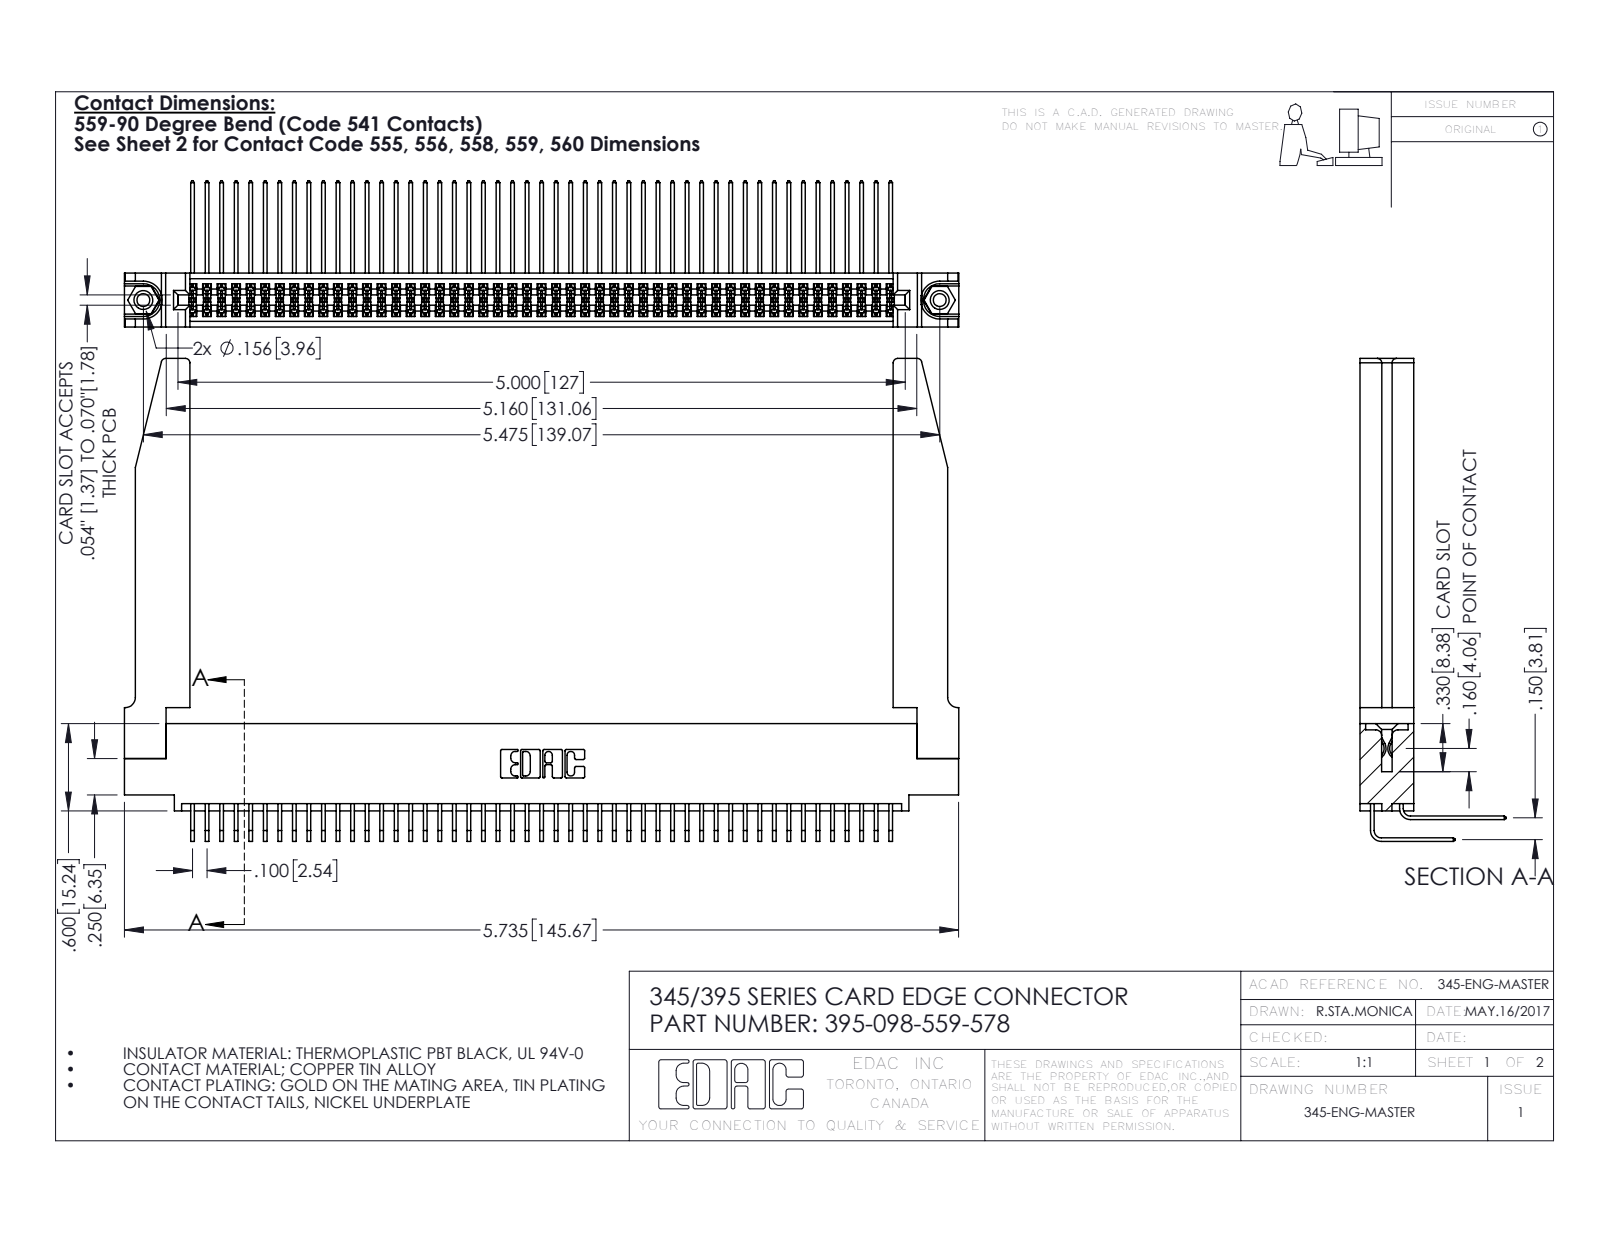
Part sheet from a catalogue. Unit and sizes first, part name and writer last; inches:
Units: inches
Overall size (bounding box): 5.736 × 3.319 × 1.005
Round holes (diameter × count): ⌀0.089 ×2, ⌀0.125 ×2, ⌀0.156 ×2, ⌀0.064 ×1
Round bosses / shafts (diameter × count): ⌀0.155 ×2
Partial cylindrical surfaces — rounded edges, fillets, slot ends (radius × count): R0.006 ×147, R0.01 ×22, R0.03 ×8, R0.007 ×6, R0.031 ×6, R0.026 ×3, R0.014 ×2, R0.019 ×2
Main face-to-face distances: 0.072, 0.37, 0.298, 0.098, 0.272, 0.025, 0.2, 0.225, 0.175, 0.15
Hole centre spacings: 0.27, 5.239, 5.475
Volume: 1.372 in³ · Surface area: 48.78 in²
Bodies: 103 solids, 5460 faces (3656 planar, 1752 cylindrical, 52 other)
Part name (STEP PRODUCT): 345-292-001_559 Tail - 2; 345-292-001_558 559 Tail - 1; 345-250-001_345-250-001-102; 345-220-078_345-220-078 (+2 more)
STEP written by: SolidWorks 2016 (CONFIG_CONTROL_DESIGN)
